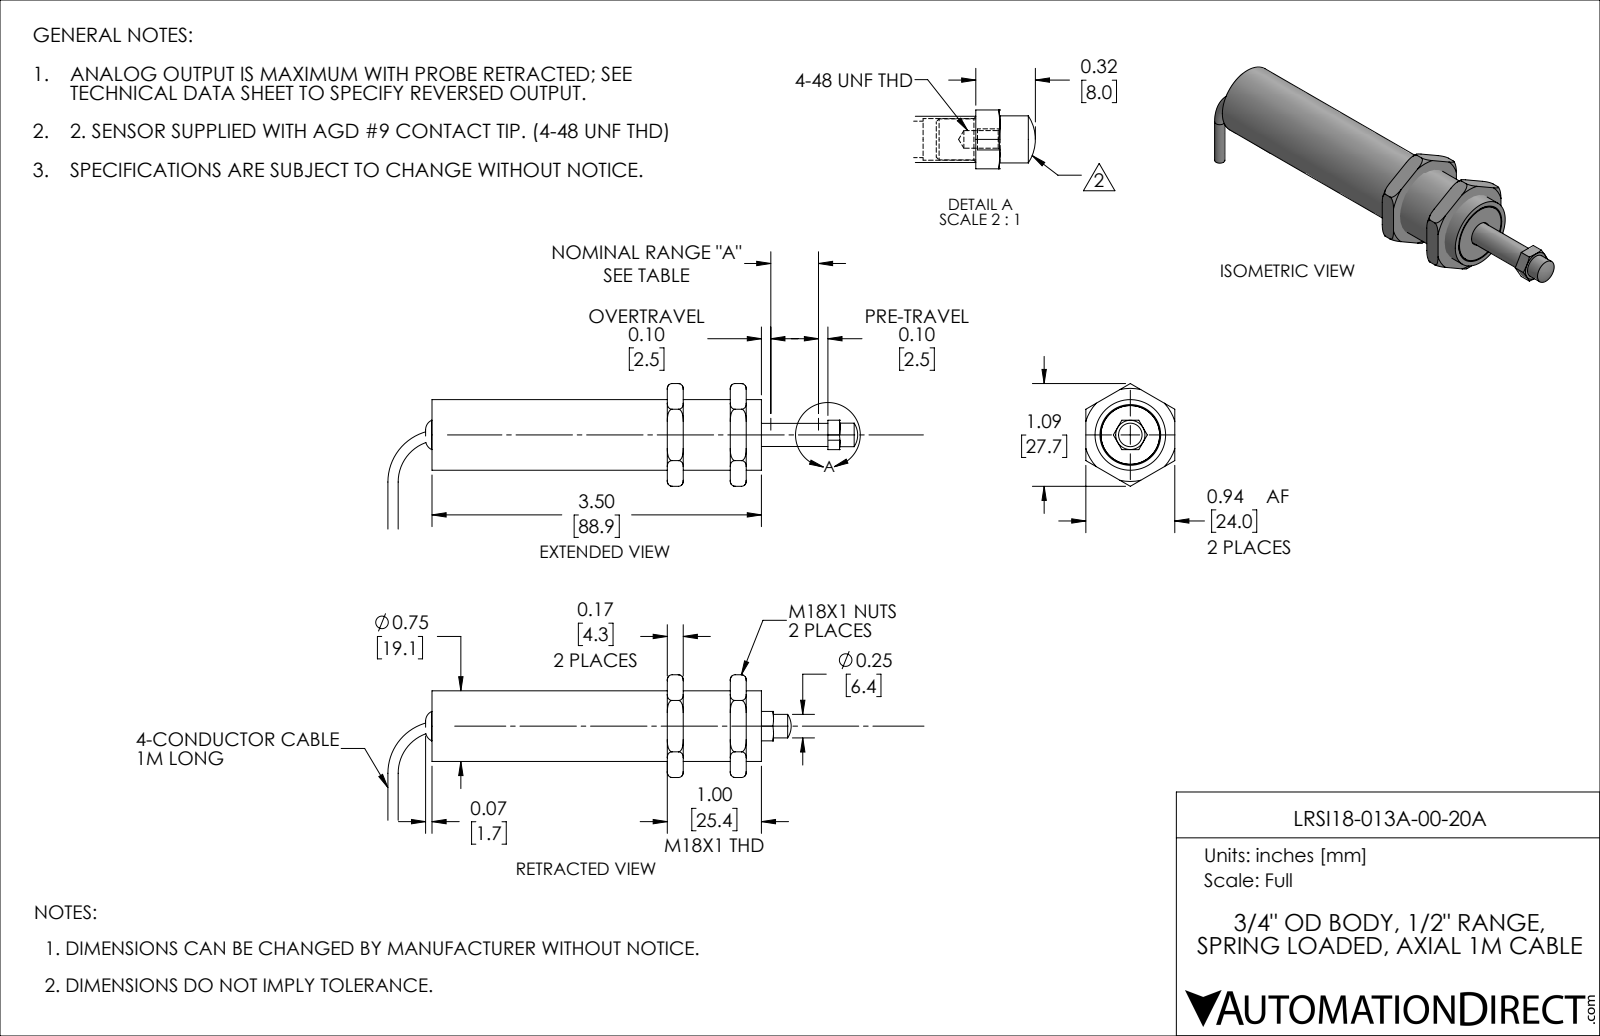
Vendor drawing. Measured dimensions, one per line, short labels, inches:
name: LRSI18-013A-00-20A
written by: SolidWorks 2019 (AUTOMOTIVE_DESIGN)
unit: in
bodies: 11 solids, 115 faces (48 planar, 26 cylindrical, 41 other)
size: 4.285 × 1.546 × 0.945
volume: 0.904 in³; area: 27.36 in²
holes: 1× ⌀0.093, 1× ⌀0.109, 1× ⌀0.188, 1× ⌀0.261, 1× ⌀0.307, 1× ⌀0.5, 1× ⌀0.62, 1× ⌀0.625, 1× ⌀0.65, 1× ⌀0.665, 1× ⌀0.71, 1× ⌀0.725
bosses: 1× ⌀0.75, 1× ⌀0.7, 1× ⌀0.685, 1× ⌀0.624, 1× ⌀0.25, 1× ⌀0.218, 1× ⌀0.112, 1× ⌀0.109
face distances: 0.669, 0.169, 0.945, 2.864, 1.864, 2.533, 1, 0.331, 2.033, 2.703
